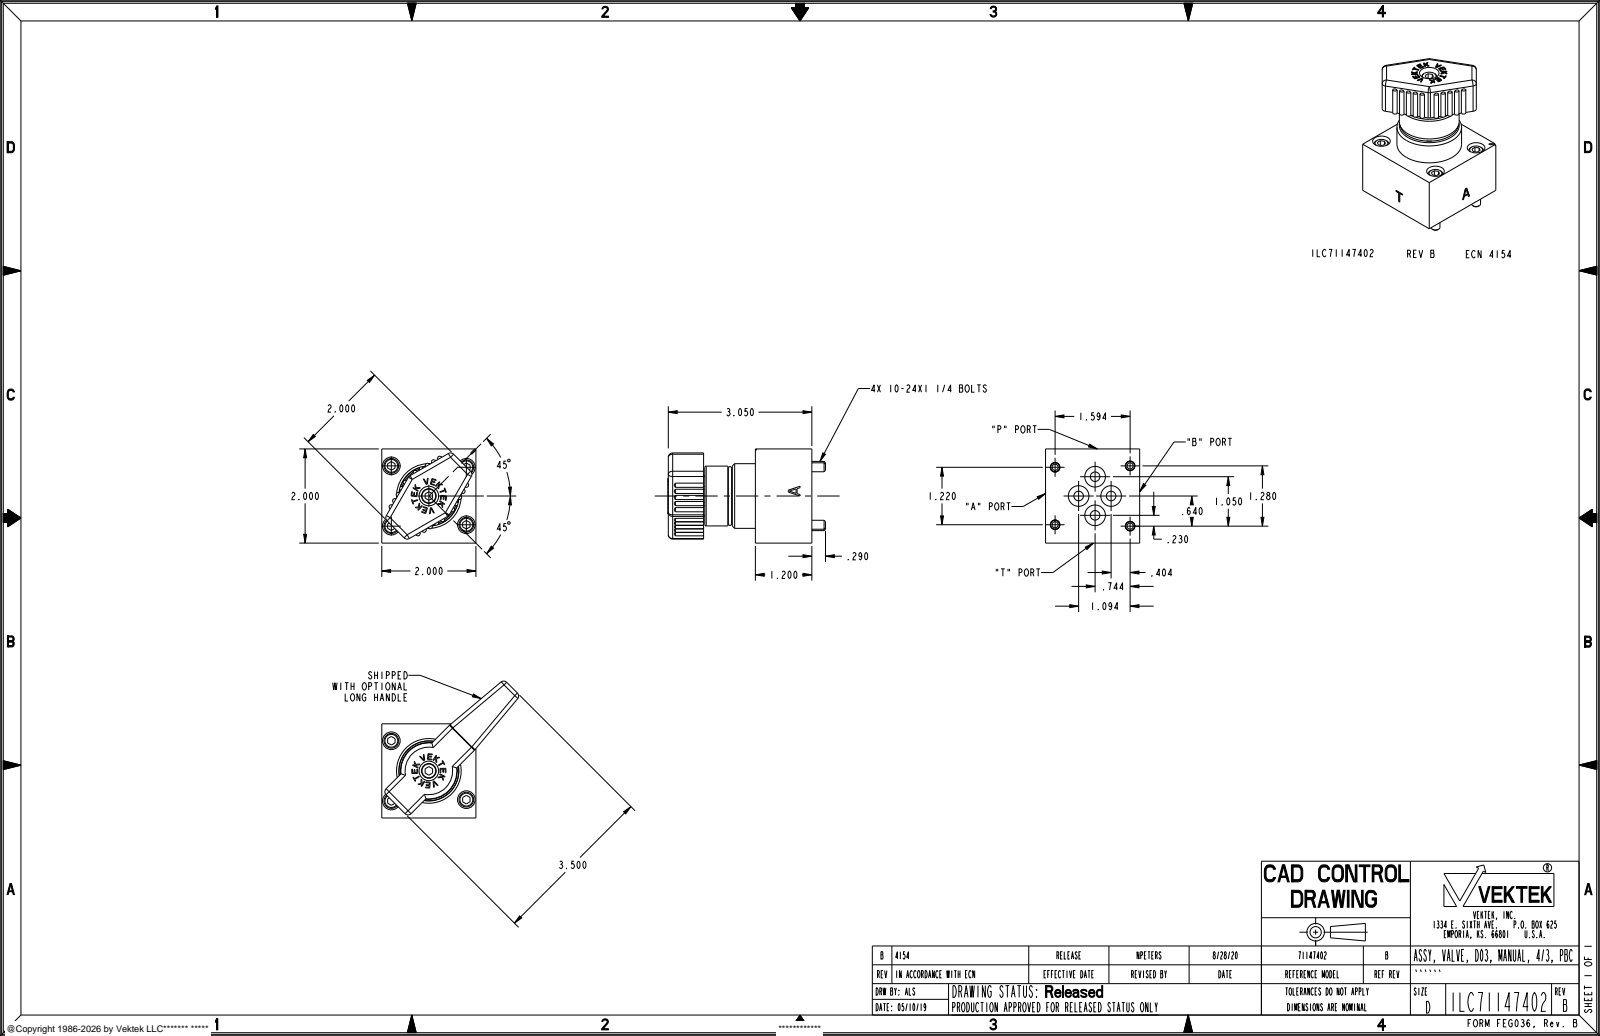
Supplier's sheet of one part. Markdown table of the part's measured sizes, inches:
| quantity | value |
| --- | --- |
| part name | ILC71147402_BASE; ILC71147402_ADAPTER; 85600903; 85600902 (+1 more) |
| STEP written by | PRO/ENGINEER BY PARAMETRIC TECHNOLOGY CORPORATION, 2013320 (AP203_CONFIGURATION_CONTROLLED_3D_DESIGN_OF_MECHANICAL_PARTS_AND_ASSEMBLIES_MIM_LF) |
| units | inches |
| bodies | 5 solids, 1648 faces (1376 planar, 190 cylindrical, 82 other) |
| overall size | 3.35 × 2.908 × 2.908 |
| volume | 8.361 in³ |
| surface area | 61.92 in² |
| round holes (diameter × count) | 0.203 × 9, 0.201 × 4, 0.375 × 4, 0.438 × 4, 0.199 × 2, 0.204 × 1, 0.205 × 1, 0.415 × 1, 0.5 × 1 |
| round bosses / shafts (diameter × count) | 0.19 × 5, 0.313 × 4, 1.373 × 1, 1.27 × 1, 0.312 × 1 |
| partial cylindrical surfaces (radius × count) | 0.09 × 23, 0.048 × 20, 0.093 × 12, 0.03 × 10, 0.045 × 8, 0.062 × 8, 0.031 × 6, 0.12 × 4 |
| main face-to-face distances | 2, 1.2, 0.32, 1.1, 2.3, 0.1, 0.75, 1.42, 2.62, 0.425 |
| hole center spacings | 0.413, 0.437, 0.532, 0.539, 0.757, 0.779, 0.789, 0.873 |
